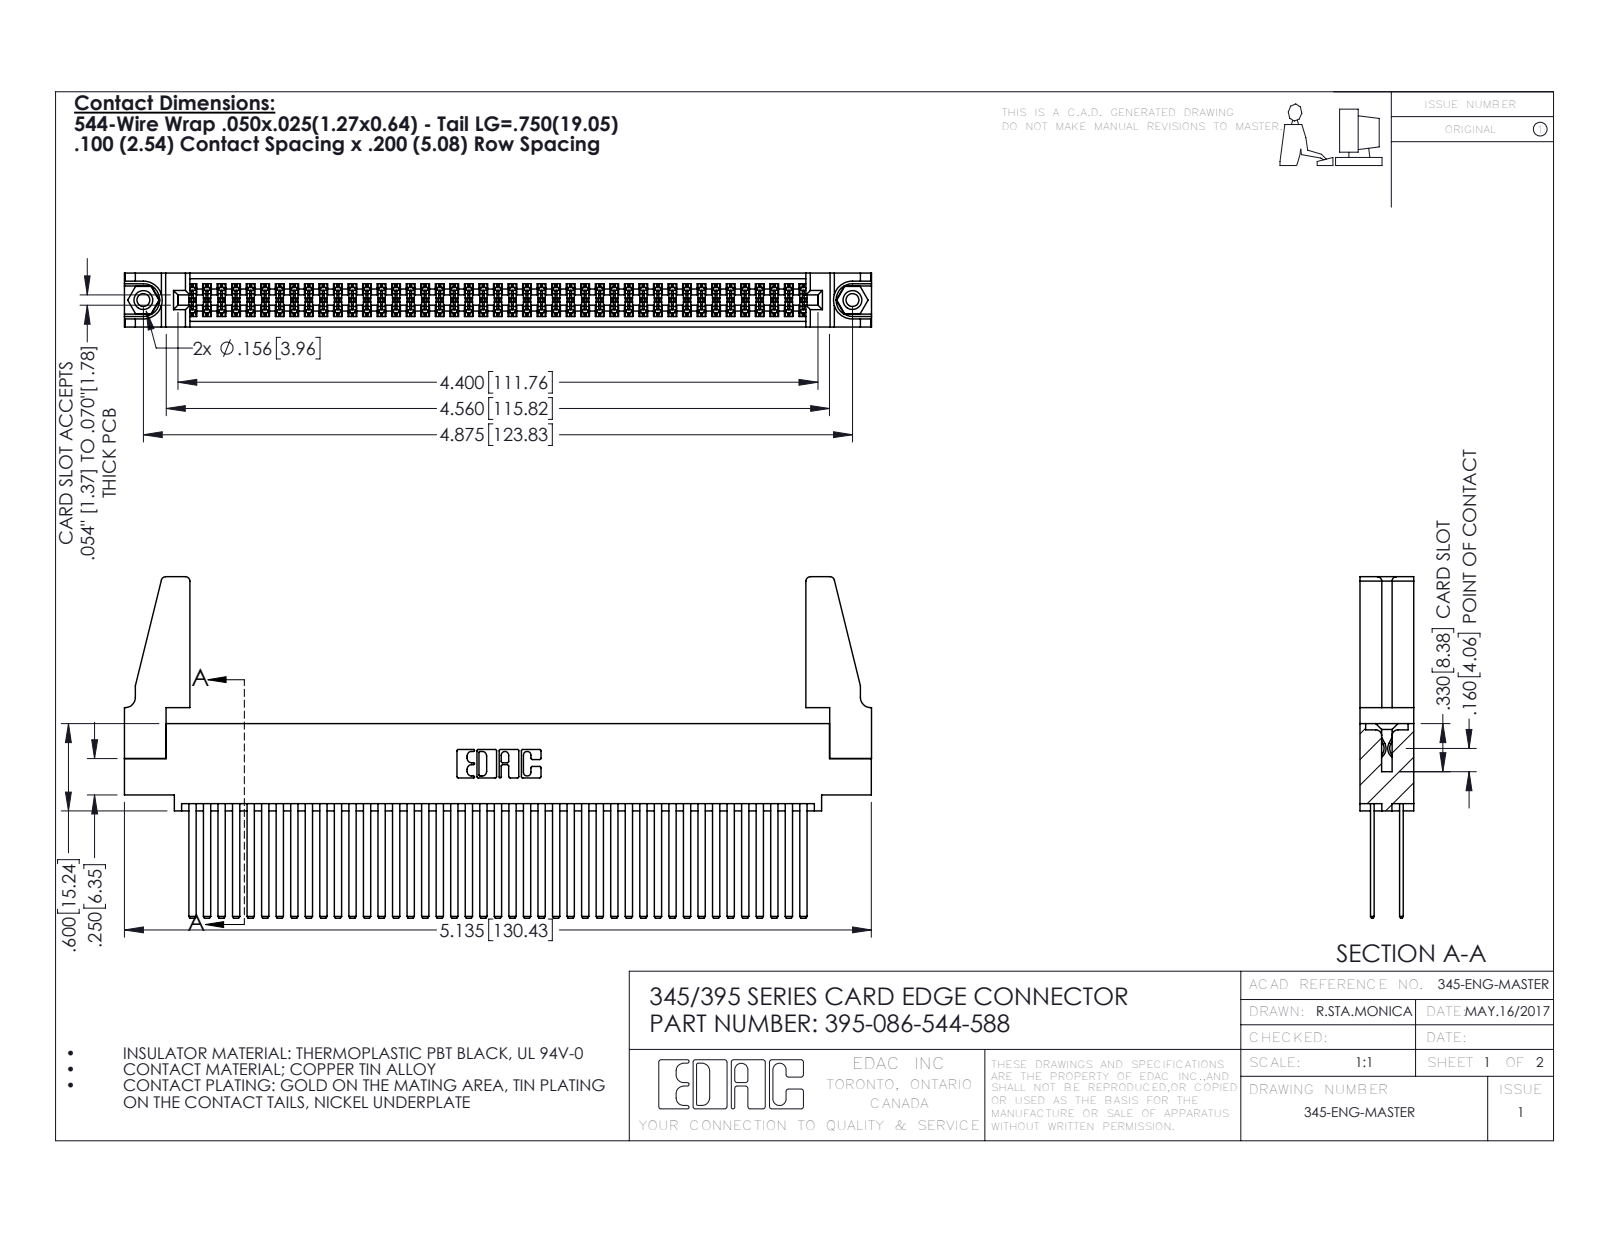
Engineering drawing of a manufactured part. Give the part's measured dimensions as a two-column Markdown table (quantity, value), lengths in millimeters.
| quantity | value |
| --- | --- |
| part name | 345 Part_0.110 Offset - 0.156 Dia-TH; 395-086-544-588; 345-250-001_345-250-001-102; 345-220-078_345-220-088 (+1 more) |
| STEP written by | SolidWorks 2016 (CONFIG_CONTROL_DESIGN) |
| units | millimeters |
| bodies | 91 solids, 4038 faces (2650 planar, 1372 cylindrical, 16 other) |
| overall size | 130.5 × 59.6 × 9.4 |
| volume | 17 060 mm³ |
| surface area | 27 190 mm² |
| round holes (diameter × count) | 2.3 × 2, 3.2 × 2, 4 × 2, 1.6 × 1 |
| round bosses / shafts (diameter × count) | 3.9 × 2 |
| partial cylindrical surfaces (radius × count) | 0.2 × 129, 0.3 × 22, 0.8 × 8, 0.2 × 6, 0.8 × 6, 0.7 × 3, 0.4 × 2, 0.5 × 2 |
| main face-to-face distances | 1.8, 7.6, 5.1, 2.5, 6.9, 0.6, 5.7, 9.4, 4.4, 3.8 |
| hole center spacings | 6.9, 117.8, 123.8 |
